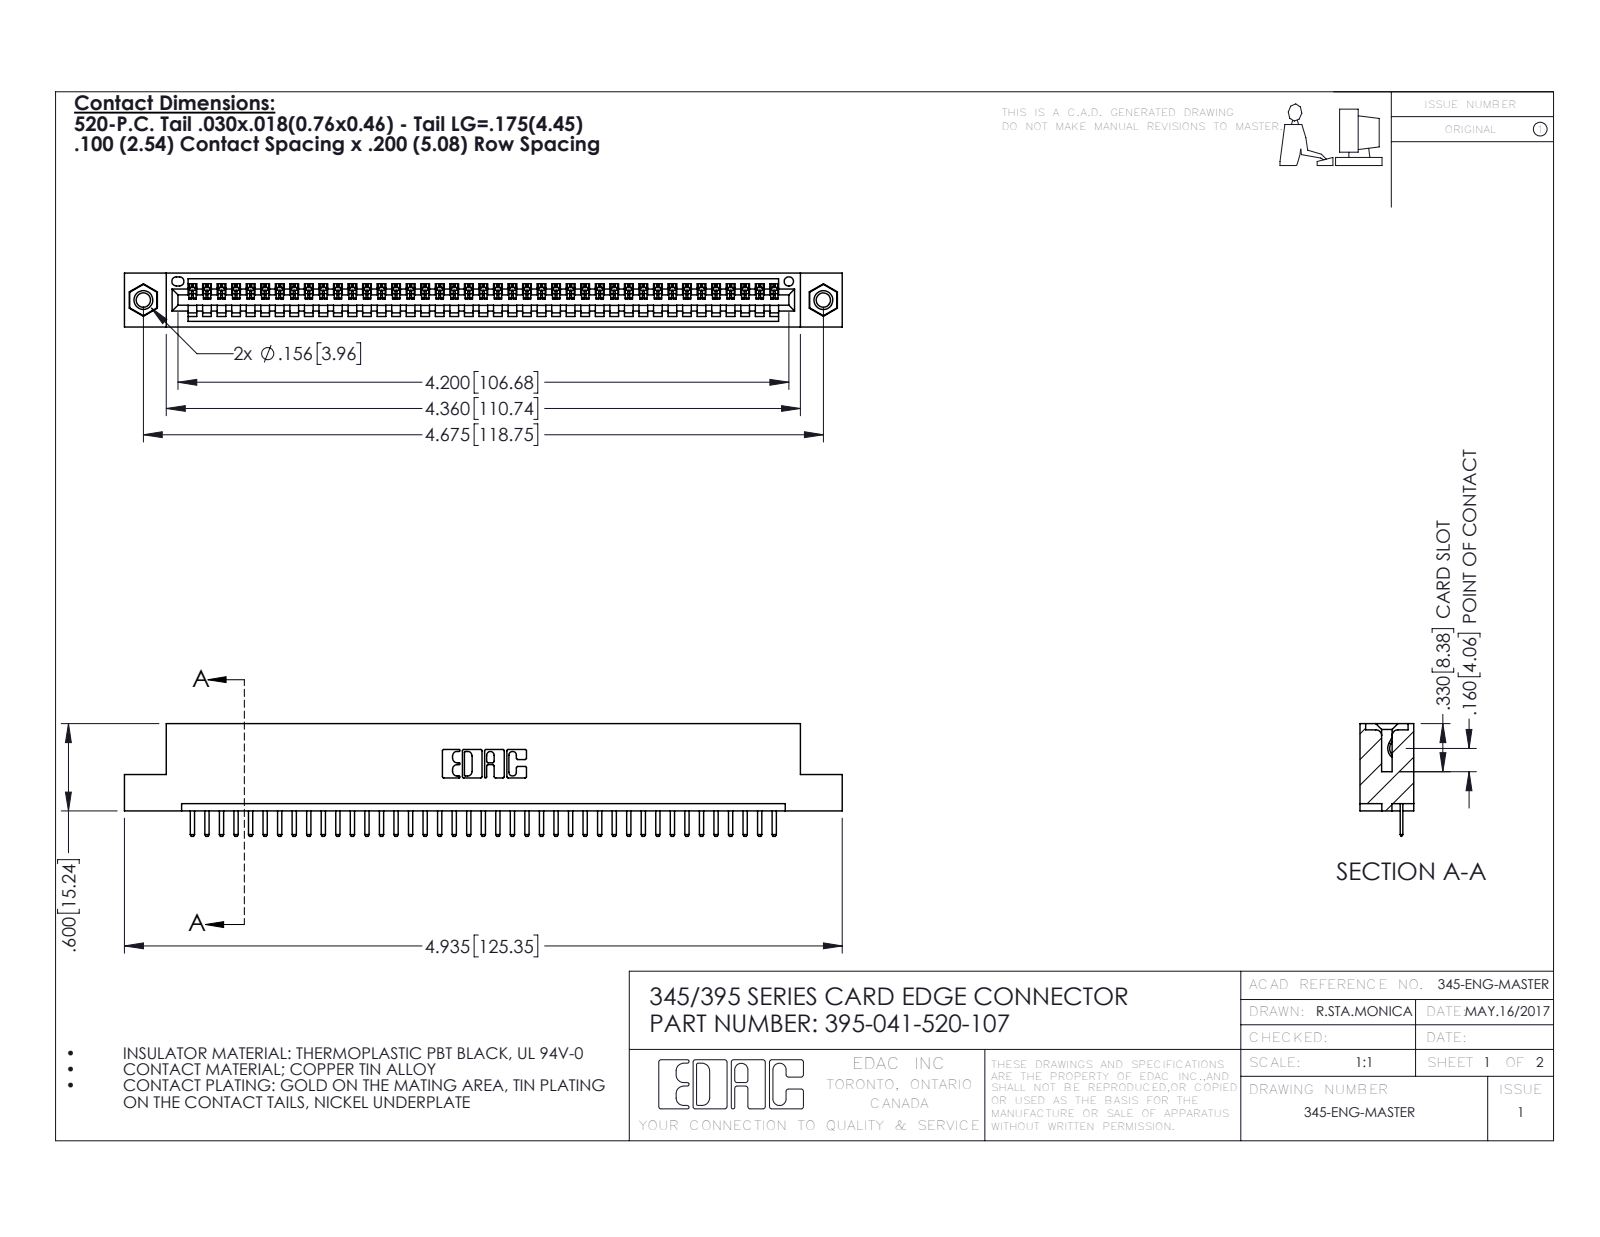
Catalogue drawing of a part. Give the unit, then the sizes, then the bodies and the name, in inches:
Units: inches
Overall size (bounding box): 4.935 × 0.775 × 0.37
Round holes (diameter × count): ⌀0.098 ×2, ⌀0.125 ×2, ⌀0.156 ×2, ⌀0.064 ×1
Round bosses / shafts (diameter × count): ⌀0.155 ×2
Partial cylindrical surfaces — rounded edges, fillets, slot ends (radius × count): R0.01 ×84, R0.006 ×82, R0.01 ×22, R0.007 ×6, R0.031 ×6, R0.026 ×3, R0.031 ×2, R0.04 ×2
Main face-to-face distances: 0.072, 0.298, 0.37, 0.2, 0.098, 0.272, 0.025, 0.225, 0.072, 0.149
Hole centre spacings: 0.27, 4.439, 4.675
Volume: 0.718 in³ · Surface area: 23.67 in²
Bodies: 44 solids, 2728 faces (1834 planar, 878 cylindrical, 16 other)
Part name (STEP PRODUCT): 345-250-001_345-250-005-103; 345-292-001_345-293-120; 395-041-520-107; 345 Part_Flush Mounting Lugs - 0.156 Dia-TI
STEP written by: SolidWorks 2016 (CONFIG_CONTROL_DESIGN)
